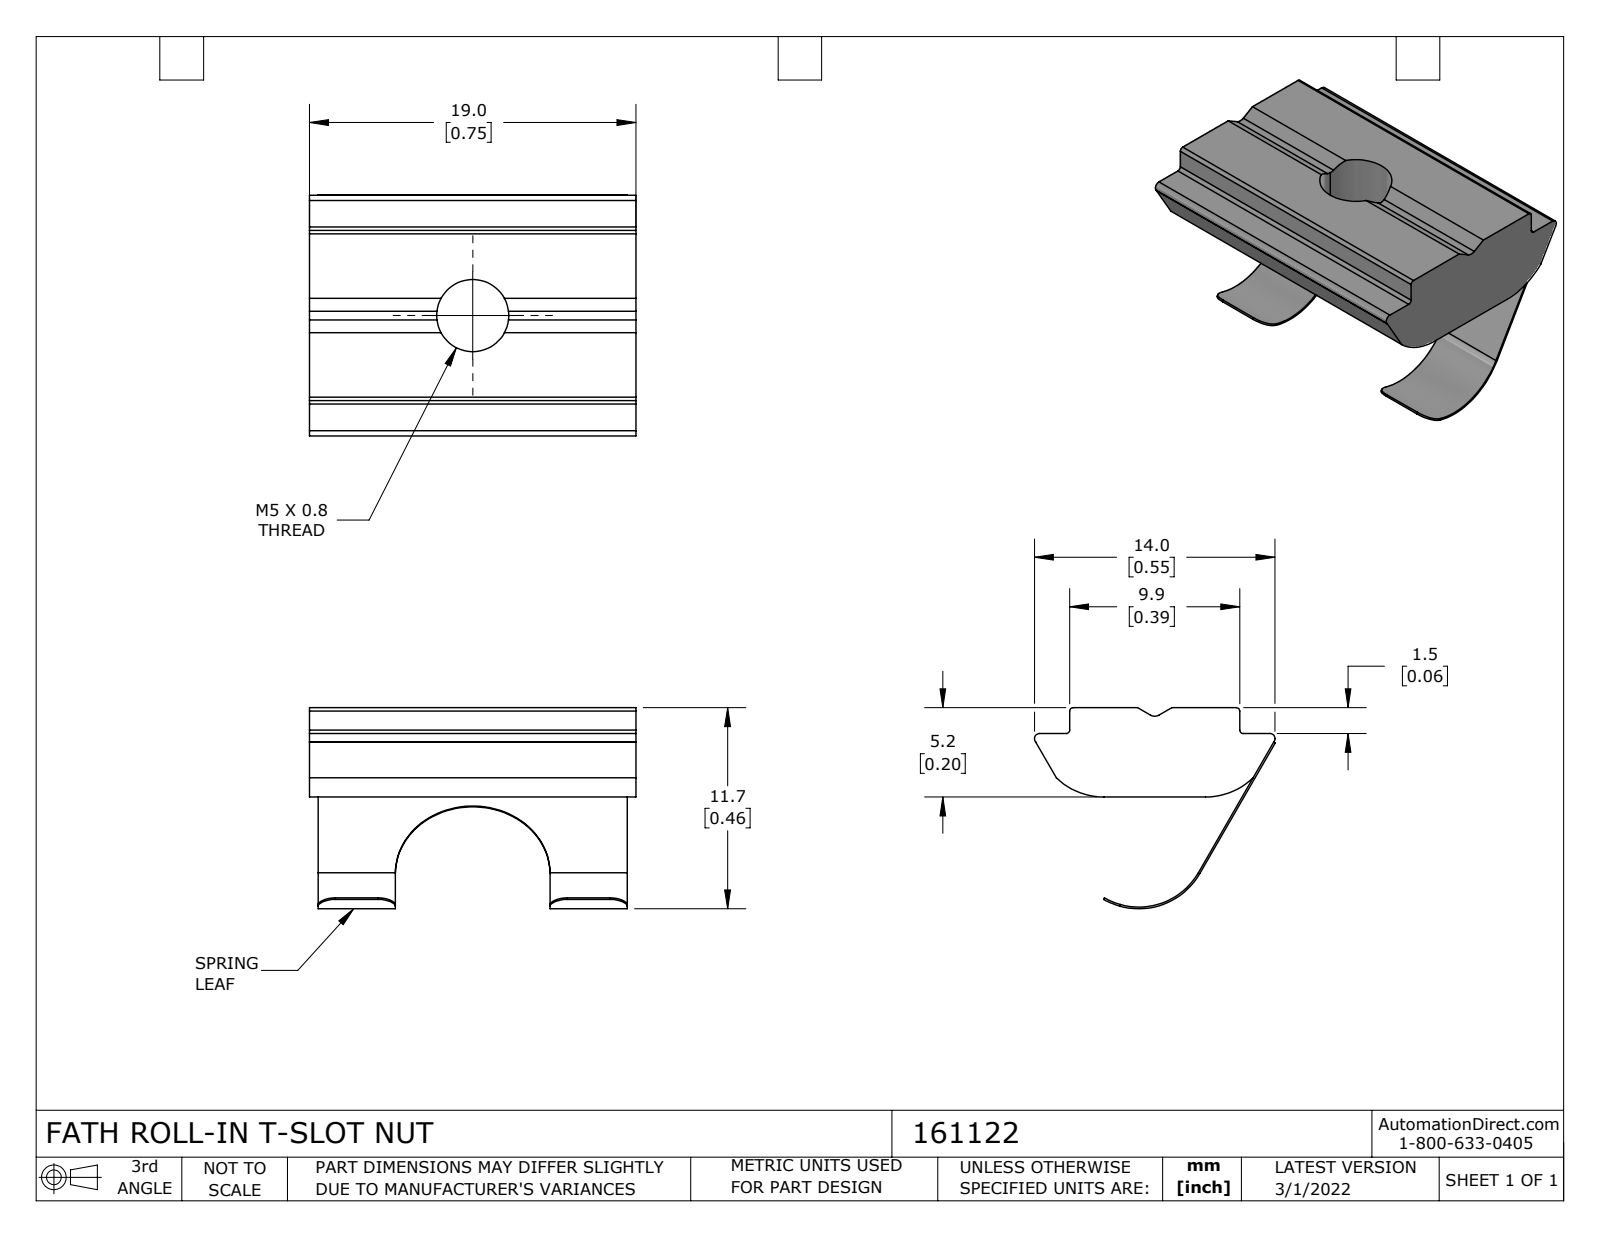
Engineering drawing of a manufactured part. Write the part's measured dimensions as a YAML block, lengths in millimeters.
part_name: "161122"
step_written_by: "SolidWorks 2021 (CONFIG_CONTROL_DESIGN)"
units: millimeters
bodies: {solids: 1, faces: 48, planar: 25, cylindrical: 23, other: 0}
overall_size: [19, 14.02, 11.7]
volume: 1059
surface_area: 1099
round_holes:
  - {diameter: 4.2, count: 1}
partial_cylinders:
  - {radius: 0.2, count: 4}
  - {radius: 1, count: 4}
  - {radius: 0.3, count: 3}
  - {radius: 4, count: 3}
  - {radius: 0.5, count: 1}
  - {radius: 4.1, count: 1}
  - {radius: 4.5, count: 1}
face_to_face_distances: [5.2, 3.7, 1.5, 19, 9.9, 0.5, 18.5, 2.24, 18, 5]
